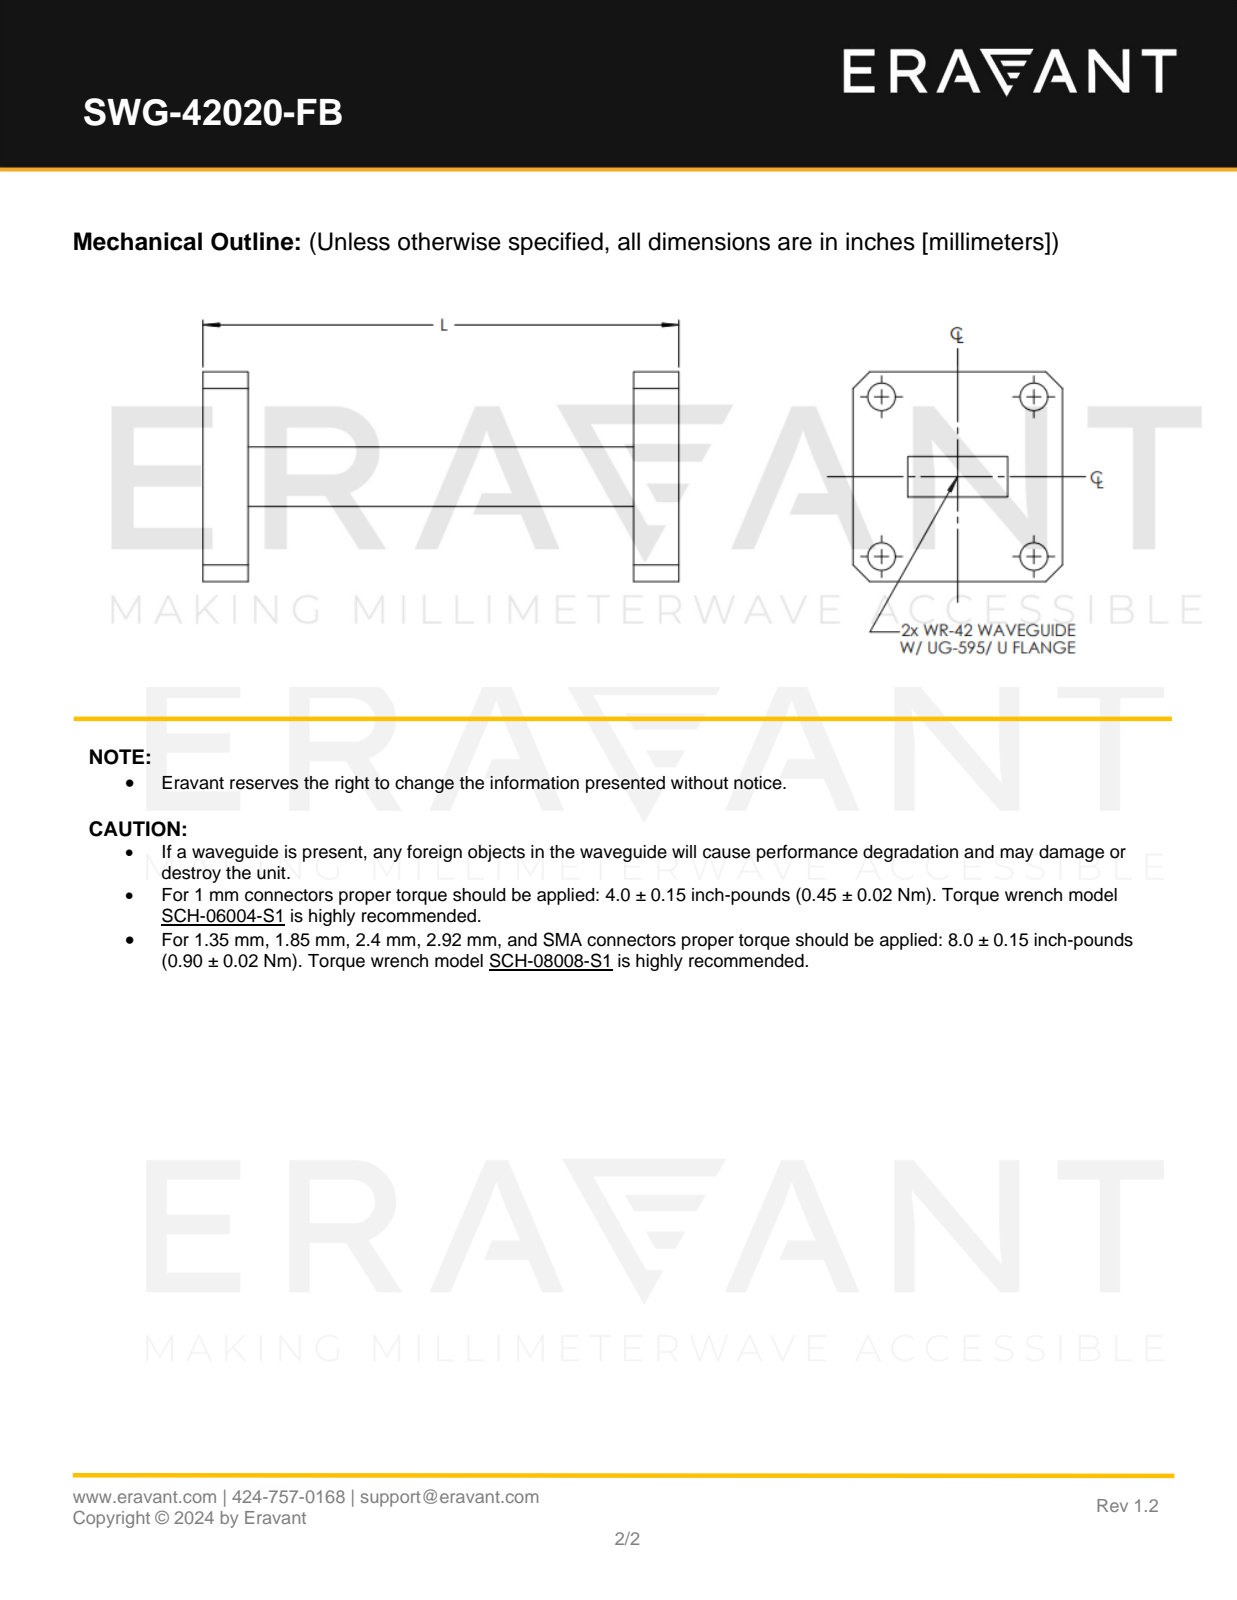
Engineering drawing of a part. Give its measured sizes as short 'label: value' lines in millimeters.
name: SWG-42020-F1
written by: SolidWorks 2013 (CONFIG_CONTROL_DESIGN)
unit: mm
bodies: 1 solid, 44 faces (28 planar, 16 cylindrical, 0 other)
size: 50.8 × 22.4 × 22.4
volume: 5 470 mm³; area: 5 881 mm²
holes: 4× ⌀2.9
face distances: 4.8, 1, 5.3, 46, 4.3, 6.4, 1, 11.7, 50.8, 41.1
hole spacings: 16.3, 17, 23.5
